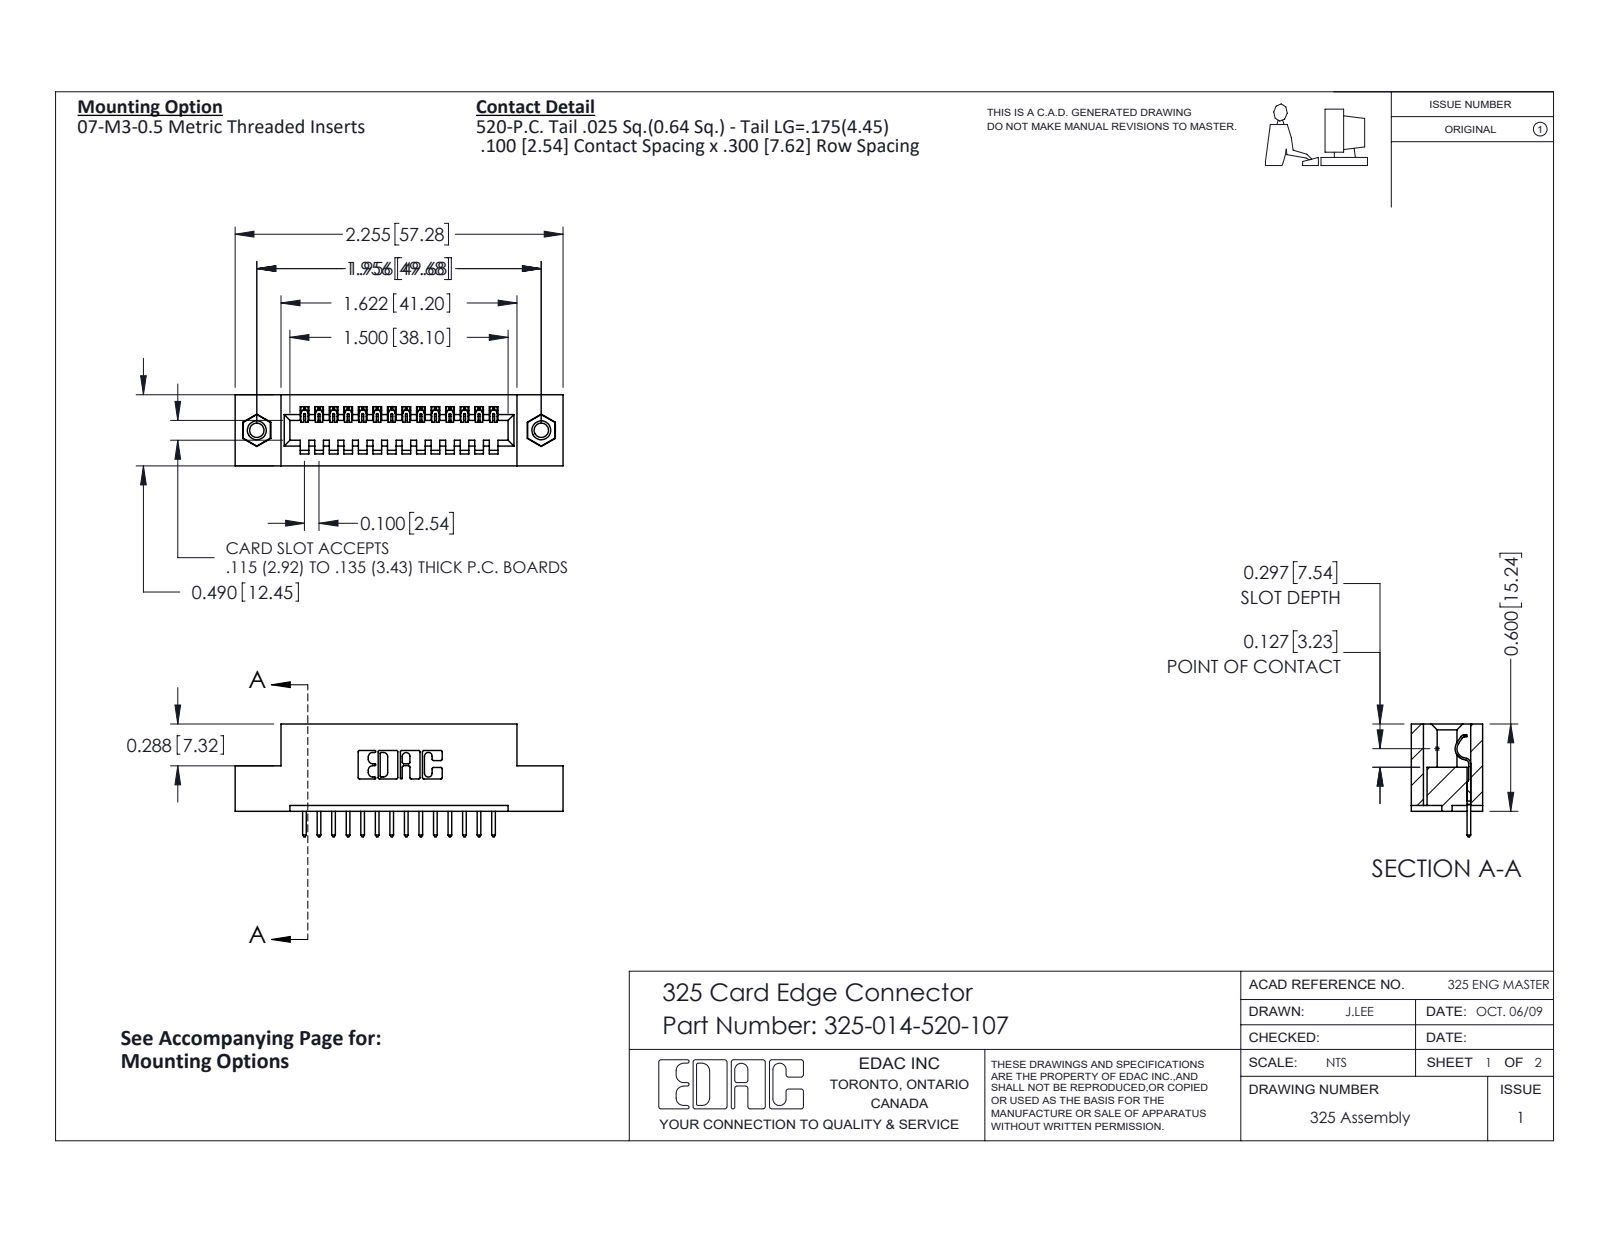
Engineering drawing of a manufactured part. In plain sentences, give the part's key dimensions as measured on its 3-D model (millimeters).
The part is named "325 Part_TI; 325-292-001_325-293-120; 325-014-520-107; 345-250-001_345-250-005-103". Its 3-D file was written by "SolidWorks 2016 (CONFIG_CONTROL_DESIGN)". It is 17 solids with 986 faces: 690 planar, 280 cylindrical and 16 other. Overall it measures 57.3 by 19.7 by 12.4 millimeters. Its volume is 7 000 cubic millimeters and its surface area 7 052 square millimeters. Round holes: 2 of diameter 2.5, 2 of diameter 3.2, 2 of diameter 4.1. Round bosses or shafts: 2 of diameter 3.9. Partial cylindrical surfaces (rounded edges, fillets, slot ends): 28 of radius 0.2, 28 of radius 0.3, 22 of radius 0.3, 6 of radius 0.2, 6 of radius 0.8, 3 of radius 0.7, 1 of radius 0.4, 1 of radius 0.6. The main face-to-face distances are 2.1, 10.3, 12.4, 7.6, 1, 2.5, 15.2, 2.7, 9.7, 0.6. The hole center spacings are 49.7.
